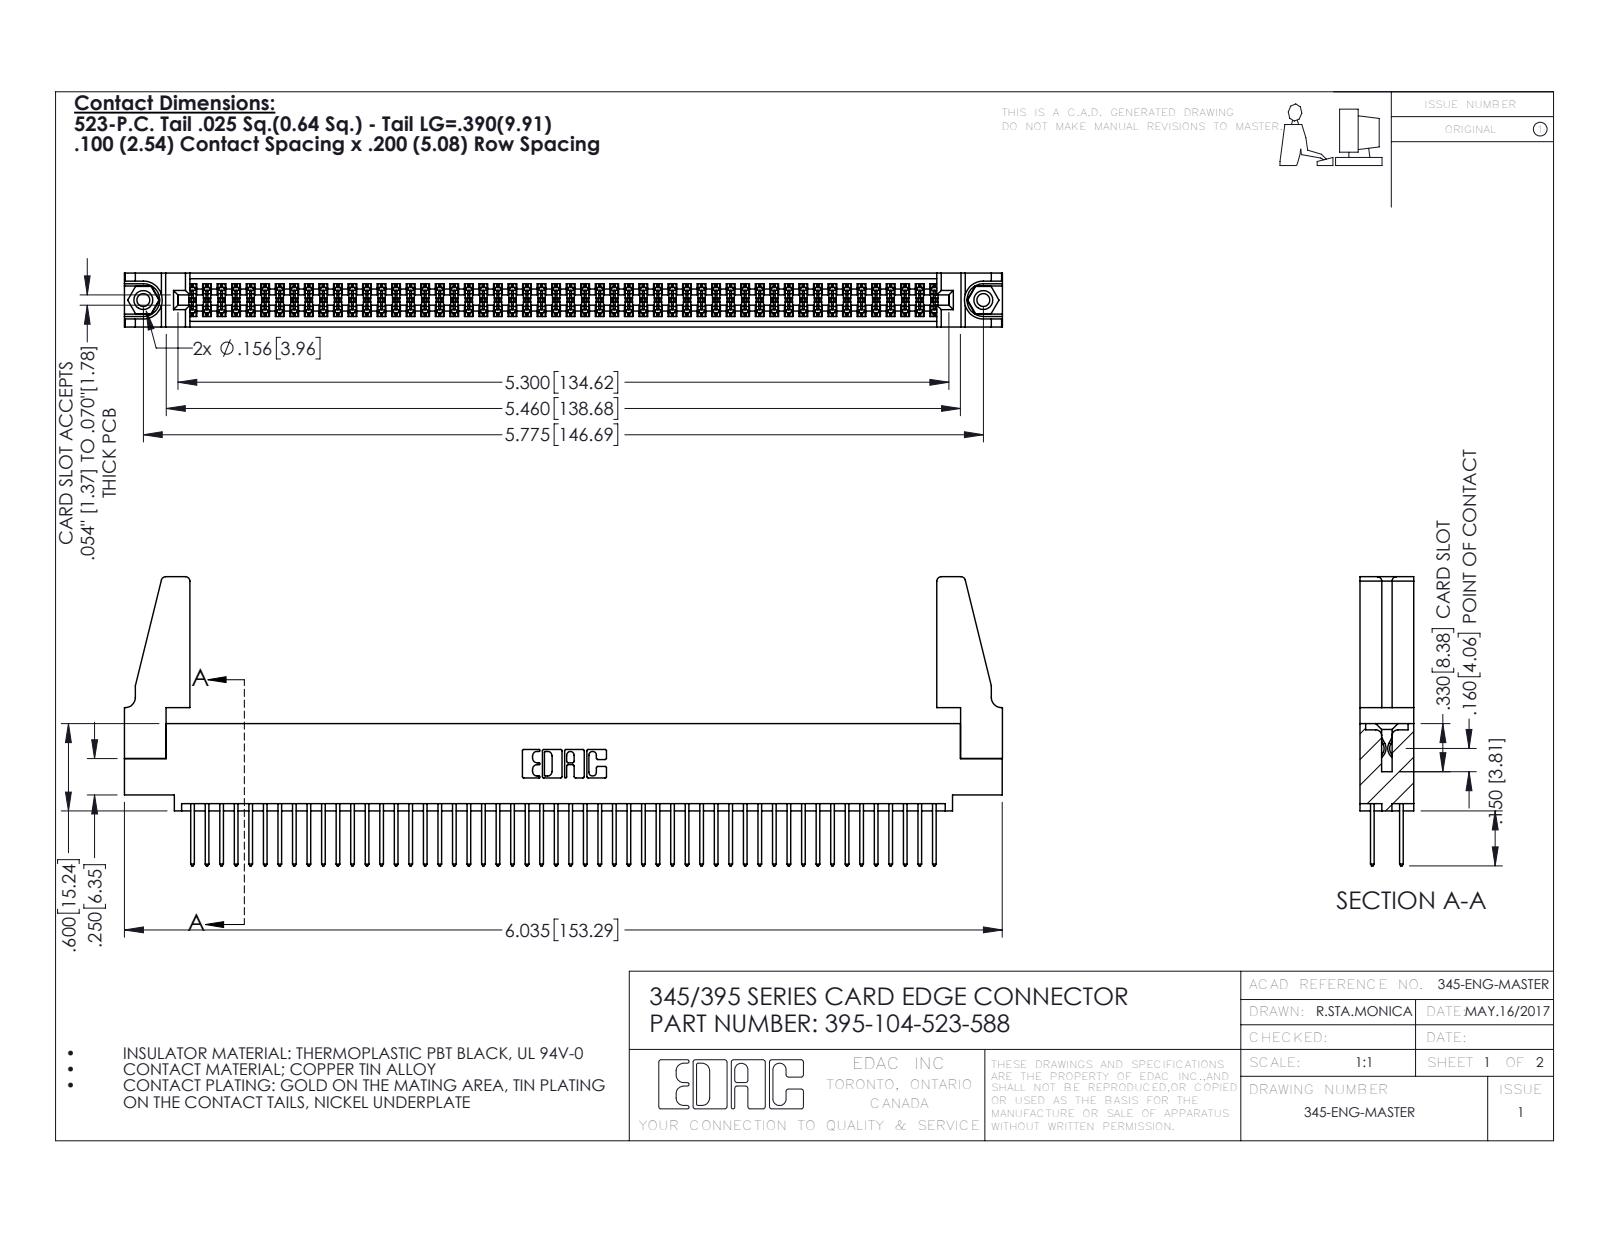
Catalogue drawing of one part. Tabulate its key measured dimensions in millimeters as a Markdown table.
| quantity | value |
| --- | --- |
| part name | 395-104-523-588; 345 Part_0.110 Offset - 0.156 Dia-TH; 345-292-001_345-293-123; 345-220-078_345-220-088 (+1 more) |
| STEP written by | SolidWorks 2016 (CONFIG_CONTROL_DESIGN) |
| units | millimeters |
| bodies | 109 solids, 5454 faces (3588 planar, 1850 cylindrical, 16 other) |
| overall size | 153.3 × 50.5 × 9.4 |
| volume | 18 390 mm³ |
| surface area | 26 720 mm² |
| round holes (diameter × count) | 2.3 × 2, 3.2 × 2, 4 × 2, 1.6 × 1 |
| round bosses / shafts (diameter × count) | 3.9 × 2 |
| partial cylindrical surfaces (radius × count) | 0.2 × 156, 0.3 × 104, 0.3 × 22, 0.8 × 8, 0.2 × 6, 0.8 × 6, 0.7 × 3, 0.4 × 2 |
| main face-to-face distances | 1.8, 7.6, 9.4, 5.1, 2.5, 6.9, 0.6, 5.7, 4.4, 3.8 |
| hole center spacings | 6.9, 140.7, 146.7 |
